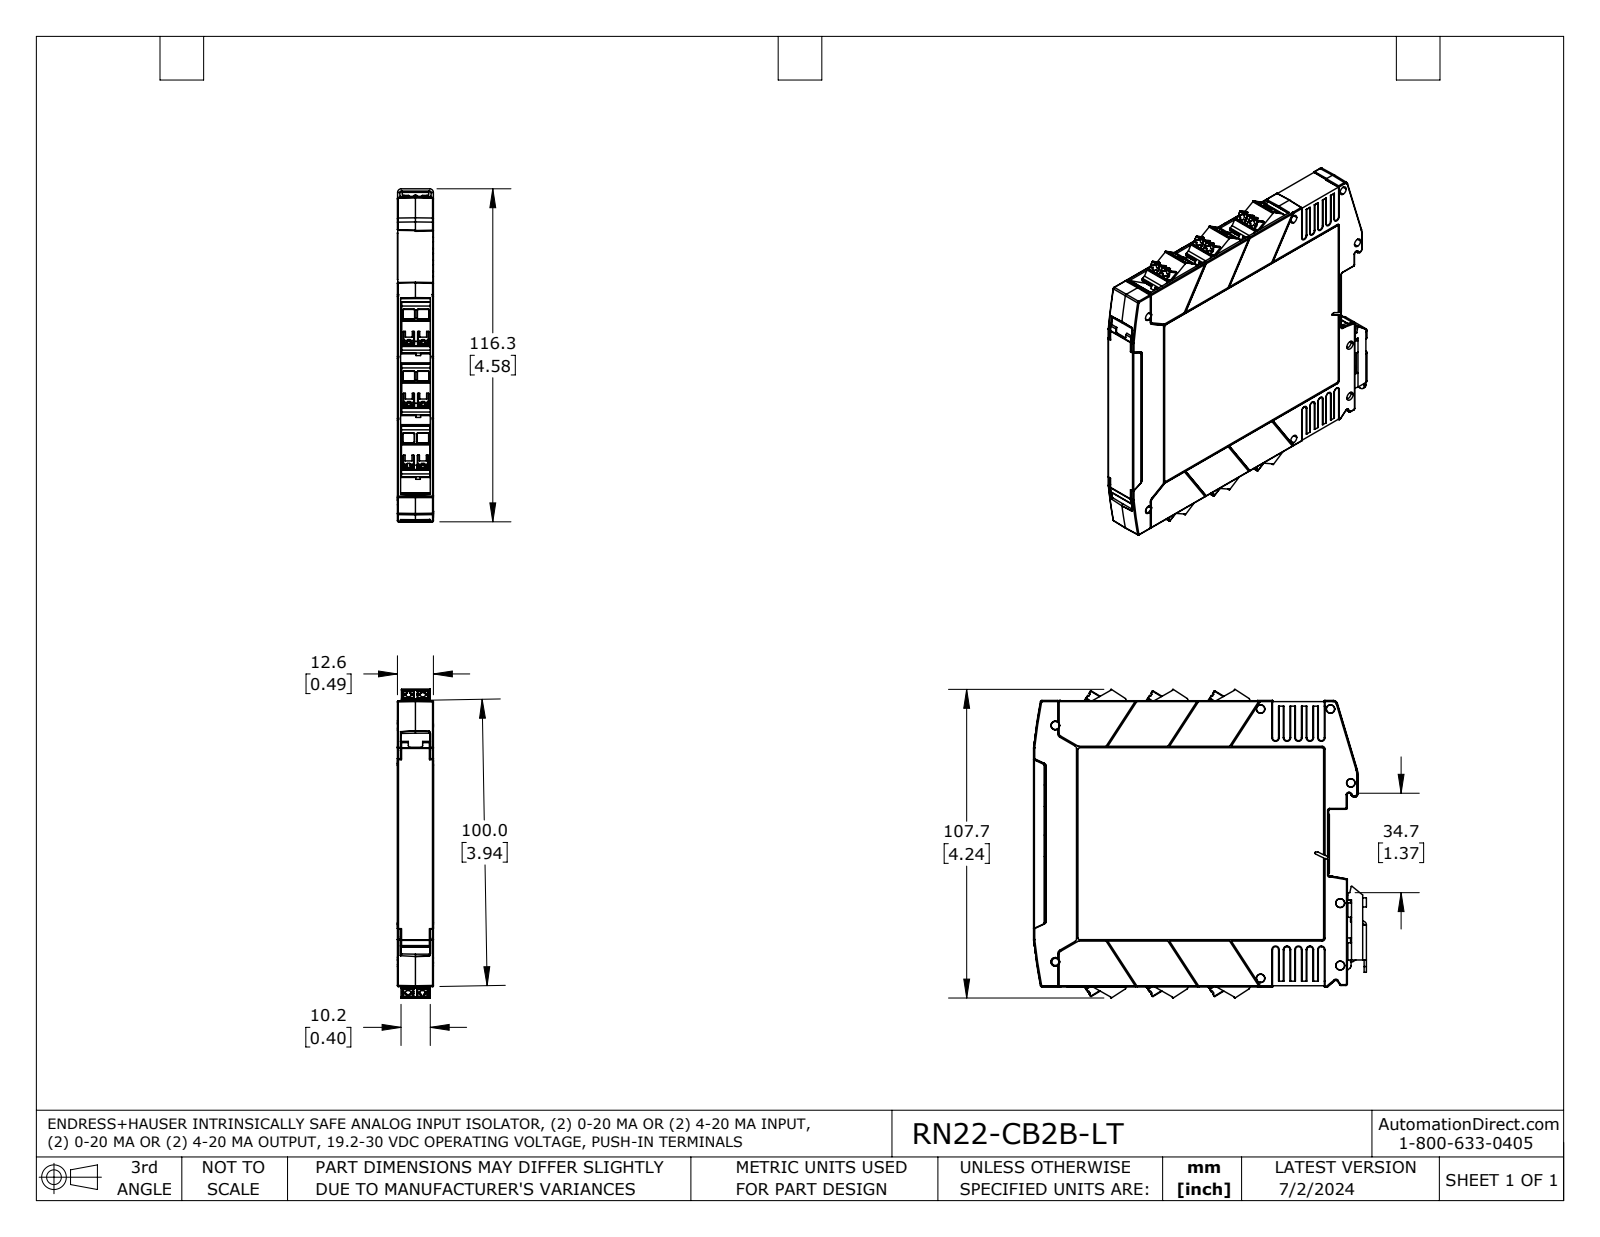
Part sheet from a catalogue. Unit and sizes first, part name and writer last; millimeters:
Units: millimetres
Overall size (bounding box): 116.3 × 107.7 × 12.6
Round holes (diameter × count): ⌀3 ×3, ⌀0.2 ×2, ⌀2.5 ×1, ⌀2.8 ×1
Partial cylindrical surfaces — rounded edges, fillets, slot ends (radius × count): R0.2 ×149, R0.5 ×71, R0.3 ×66, R1 ×28, R0.1 ×16, R2.9 ×12, R0.2 ×10, R0.6 ×10
Main face-to-face distances: 12.5, 1.1, 11.5, 1, 11.4, 1.2, 12.5, 11, 10, 0.8
Hole centre spacings: 71.9, 113.7, 19.3, 19.3, 24.4, 52.7, 52.7, 77
Volume: 133 200 mm³ · Surface area: 37 570 mm²
Bodies: 2 solids, 3045 faces (1939 planar, 765 cylindrical, 341 other)
Part name (STEP PRODUCT): RN22-CB2B-LT
STEP written by: SolidWorks 2021 (AUTOMOTIVE_DESIGN)
